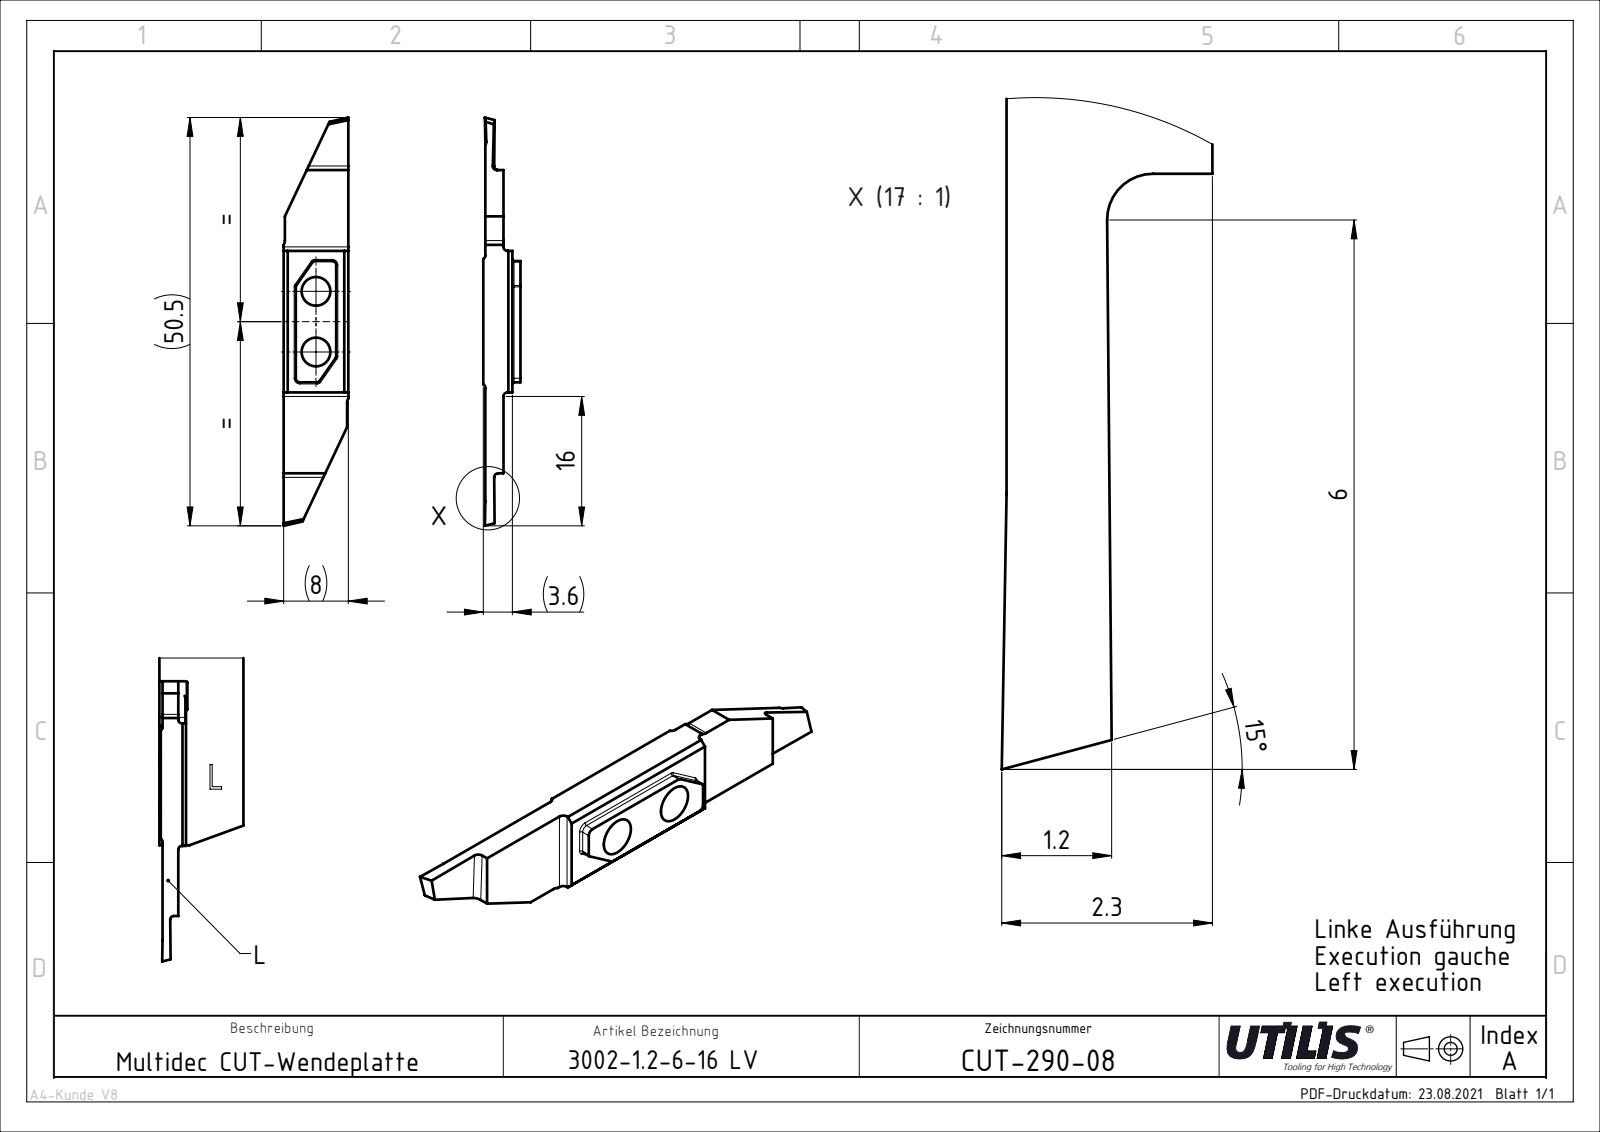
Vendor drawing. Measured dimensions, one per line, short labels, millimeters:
name: CUT-290-08
written by: SolidWorks 2016 (AUTOMOTIVE_DESIGN)
unit: mm
bodies: 1 solid, 38 faces (24 planar, 14 cylindrical, 0 other)
size: 50.5 × 8 × 3.55
volume: 794 mm³; area: 967 mm²
holes: 2× ⌀3.55
rounds: 6× R0.5, 2× R0.15, 2× R1
face distances: 2.25, 3.3, 1.05, 2.5, 3.55, 8, 18.1, 7.85, 7.7, 10
hole spacings: 7.5
